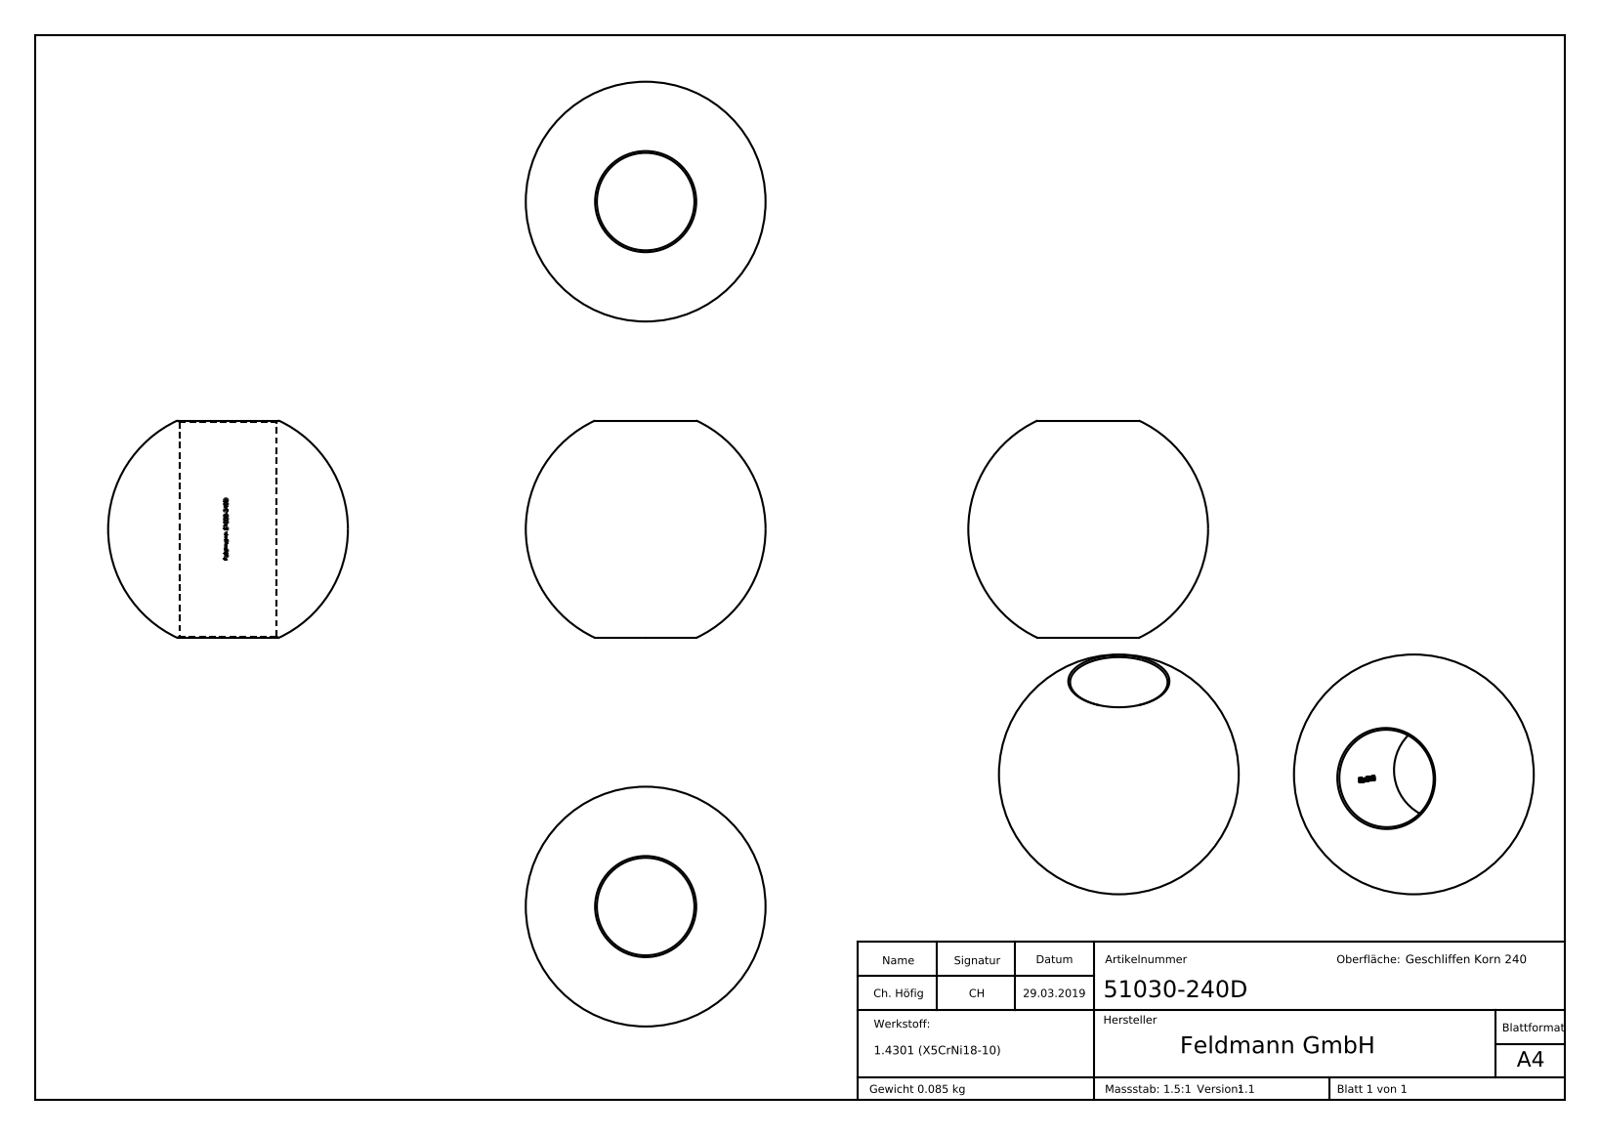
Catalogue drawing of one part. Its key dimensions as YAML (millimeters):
part_name: "51030-240D"
step_written_by: "SolidWorks 2015 (CONFIG_CONTROL_DESIGN)"
units: millimeters
bodies: {solids: 1, faces: 242, planar: 98, cylindrical: 28, other: 116}
overall_size: [30, 30, 27.2]
volume: 10777
surface_area: 3620
round_holes:
  - {diameter: 12.2, count: 1}
partial_cylinders:
  - {radius: 6.2, count: 1}
face_to_face_distances: [2.98, 1.19, 5.85, 0.66, 1.74, 0.61, 0.55, 3.48, 2.93, 0.35]
